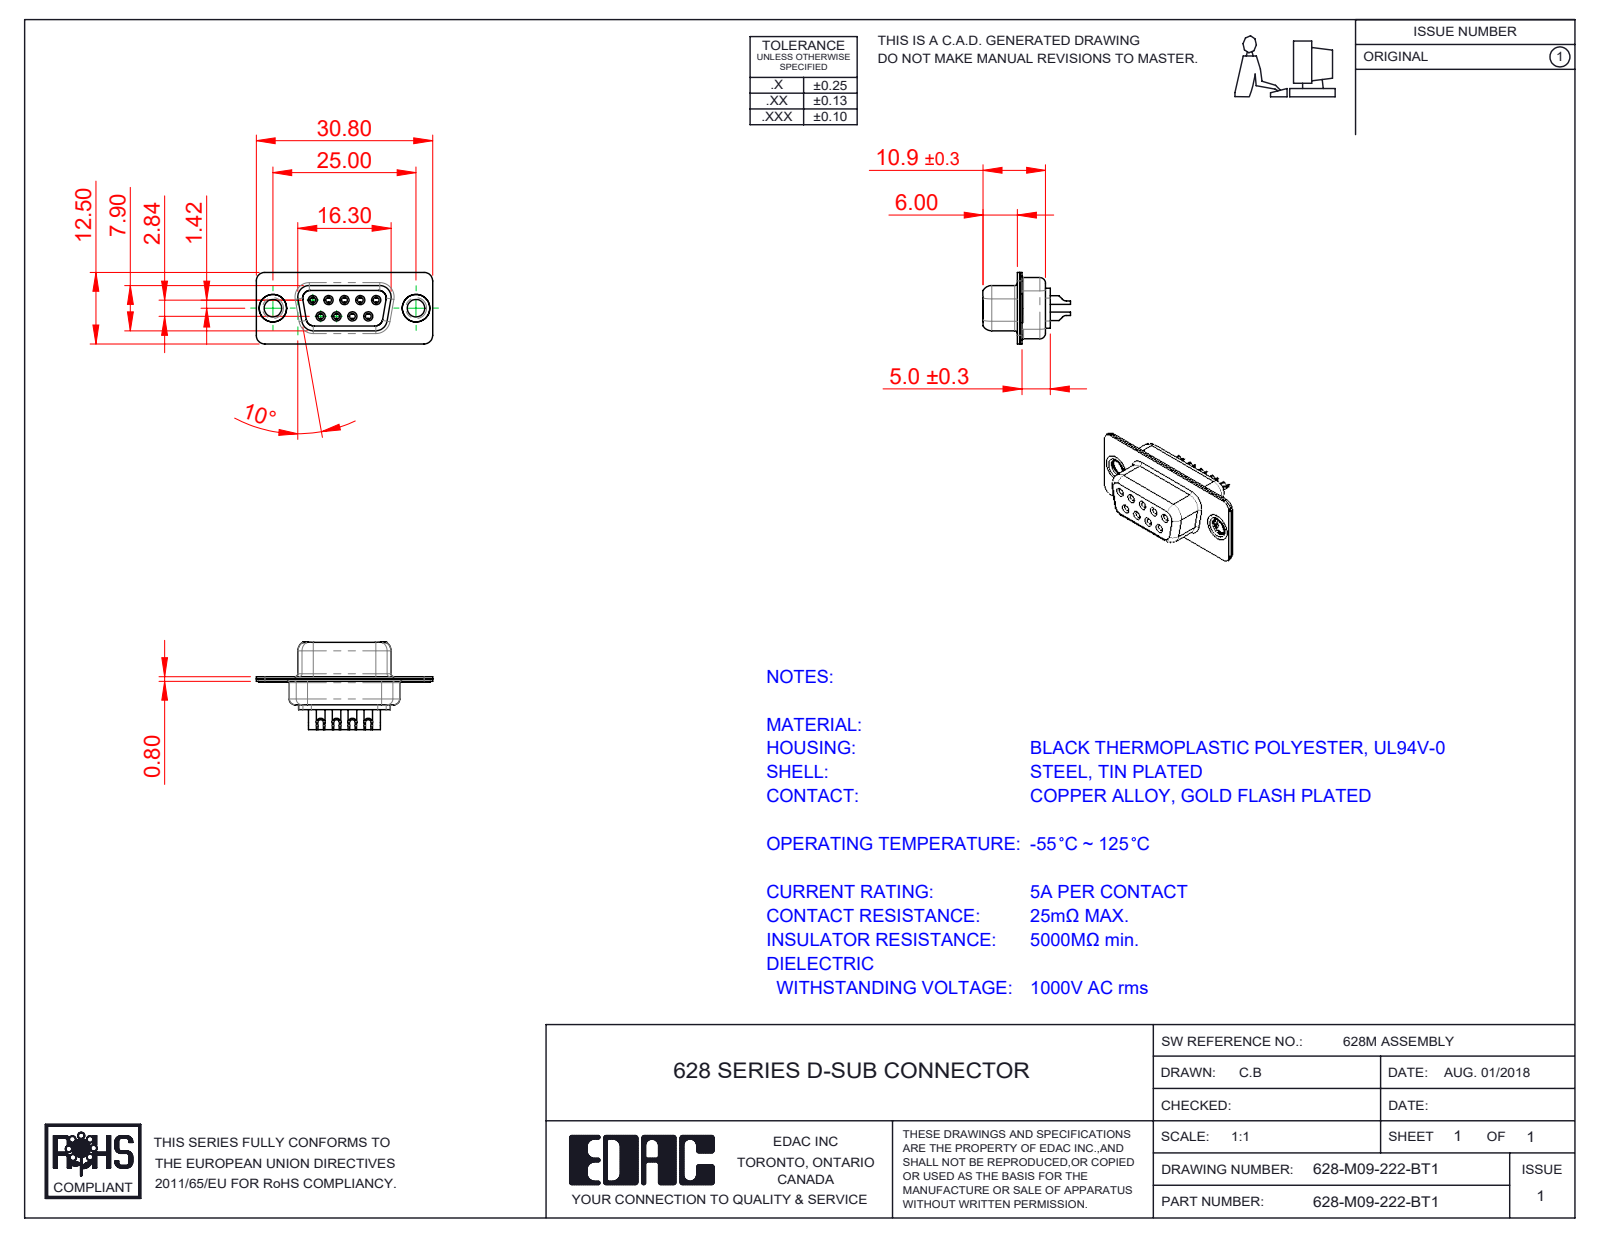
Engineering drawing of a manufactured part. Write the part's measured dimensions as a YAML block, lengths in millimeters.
part_name: "628M Contact Row 1_22; 628M Housing_09 Contacts; 628M Contact Row 2_22; 628M Shell Front_09 Contacts (+3 more)"
step_written_by: "SolidWorks 2020 (CONFIG_CONTROL_DESIGN)"
units: millimeters
bodies: {solids: 14, faces: 748, planar: 220, cylindrical: 310, other: 218}
overall_size: [30.8, 15.3, 12.5]
volume: 1637
surface_area: 4357
round_holes:
  - {diameter: 1, count: 9}
  - {diameter: 1.1, count: 9}
  - {diameter: 1.7, count: 9}
  - {diameter: 1.8, count: 9}
  - {diameter: 2, count: 9}
  - {diameter: 3.05, count: 2}
  - {diameter: 4, count: 2}
  - {diameter: 4.8, count: 2}
round_bosses_or_shafts:
  - {diameter: 2.2, count: 9}
  - {diameter: 1.6, count: 9}
  - {diameter: 1.5, count: 9}
  - {diameter: 5, count: 2}
  - {diameter: 4.9, count: 2}
  - {diameter: 3.55, count: 2}
partial_cylinders:
  - {radius: 1.5, count: 16}
  - {radius: 2, count: 12}
  - {radius: 1.35, count: 8}
  - {radius: 1.6, count: 8}
  - {radius: 1, count: 6}
  - {radius: 0.25, count: 4}
  - {radius: 0.5, count: 4}
  - {radius: 0.6, count: 4}
face_to_face_distances: [0.4, 1.4, 0.45, 8.45, 0.8, 8.9, 1.8, 7.05, 1, 0.85]
hole_center_spacings: [3.16, 2.77, 5.54, 5.03, 5.04, 8.31, 7.1, 7.48]
